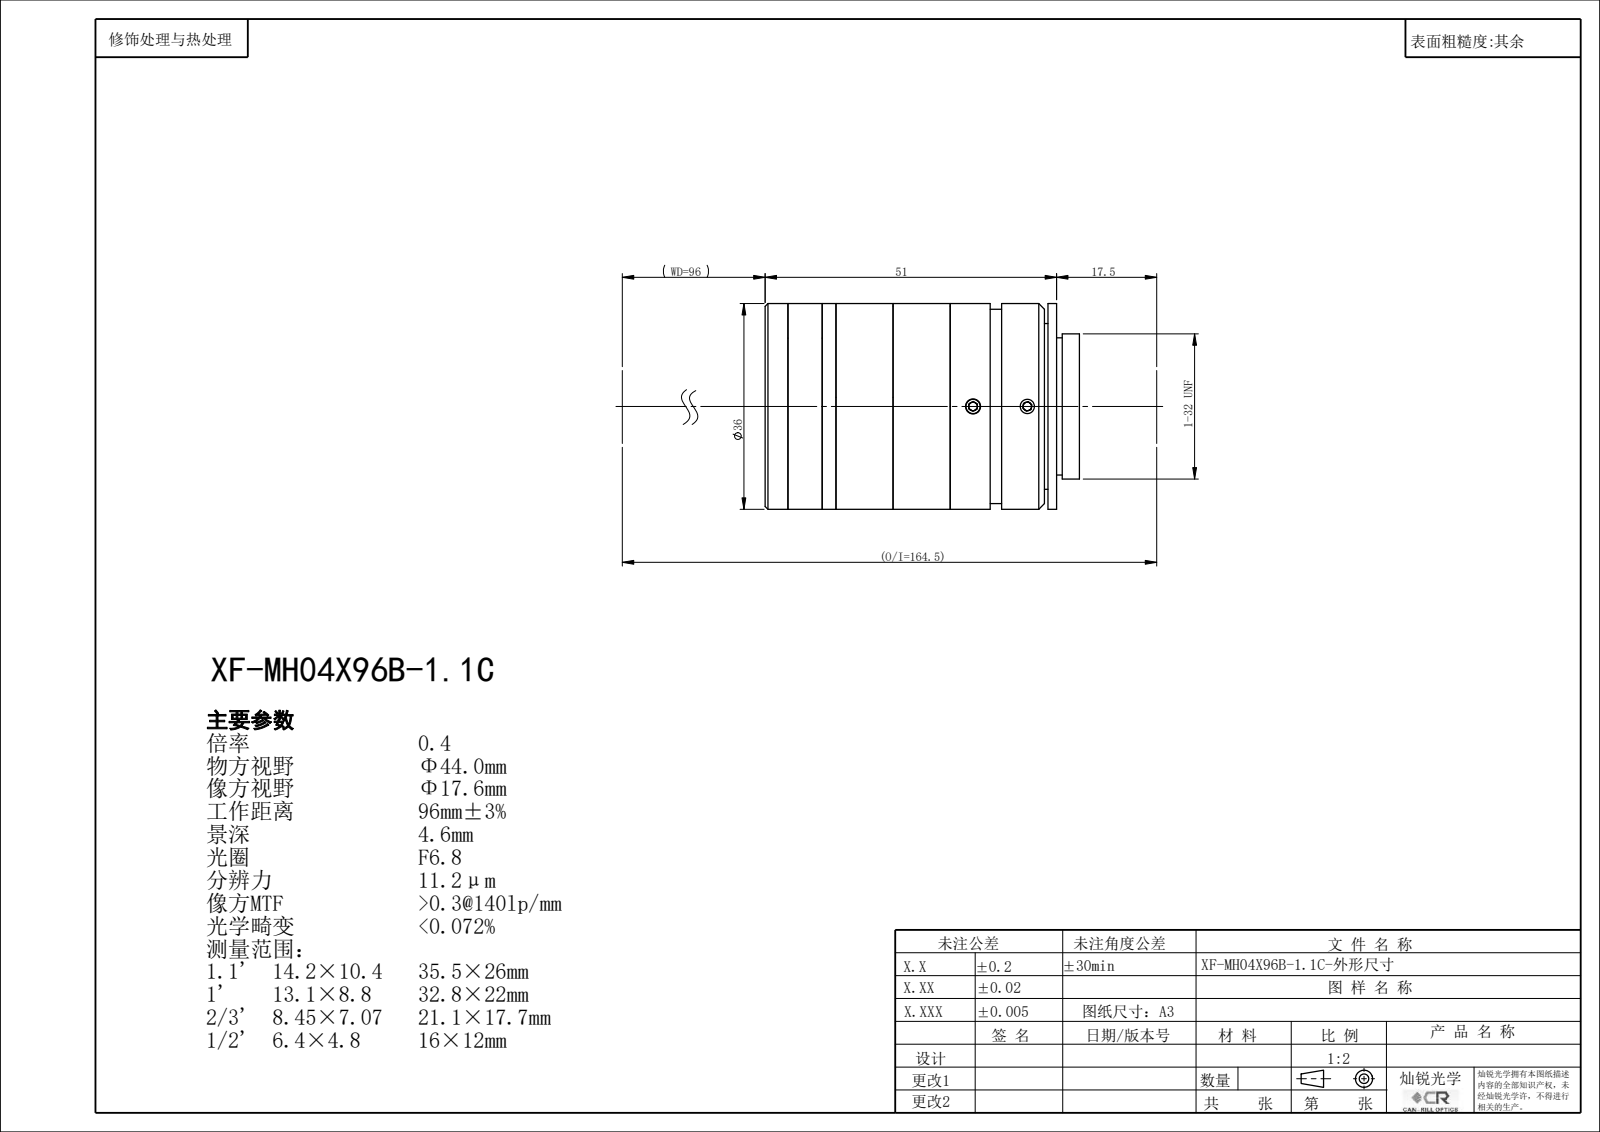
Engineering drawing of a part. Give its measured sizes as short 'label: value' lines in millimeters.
name: XF-MH04X96B-1.1C
written by: SolidWorks 2022 (CONFIG_CONTROL_DESIGN)
unit: mm
bodies: 0 solids, 159 faces (81 planar, 44 cylindrical, 34 other)
size: 55.03 × 36 × 36
holes: 3× ⌀2.5, 1× ⌀14, 1× ⌀16.4, 1× ⌀17, 1× ⌀18.4, 1× ⌀22.4, 1× ⌀24, 1× ⌀24.9, 1× ⌀26
bosses: 1× ⌀36, 1× ⌀34, 1× ⌀25.4
face distances: 10, 18.62, 51.02, 32.4, 1.5, 49.52, 17.12, 22.4, 12.4, 45.02
